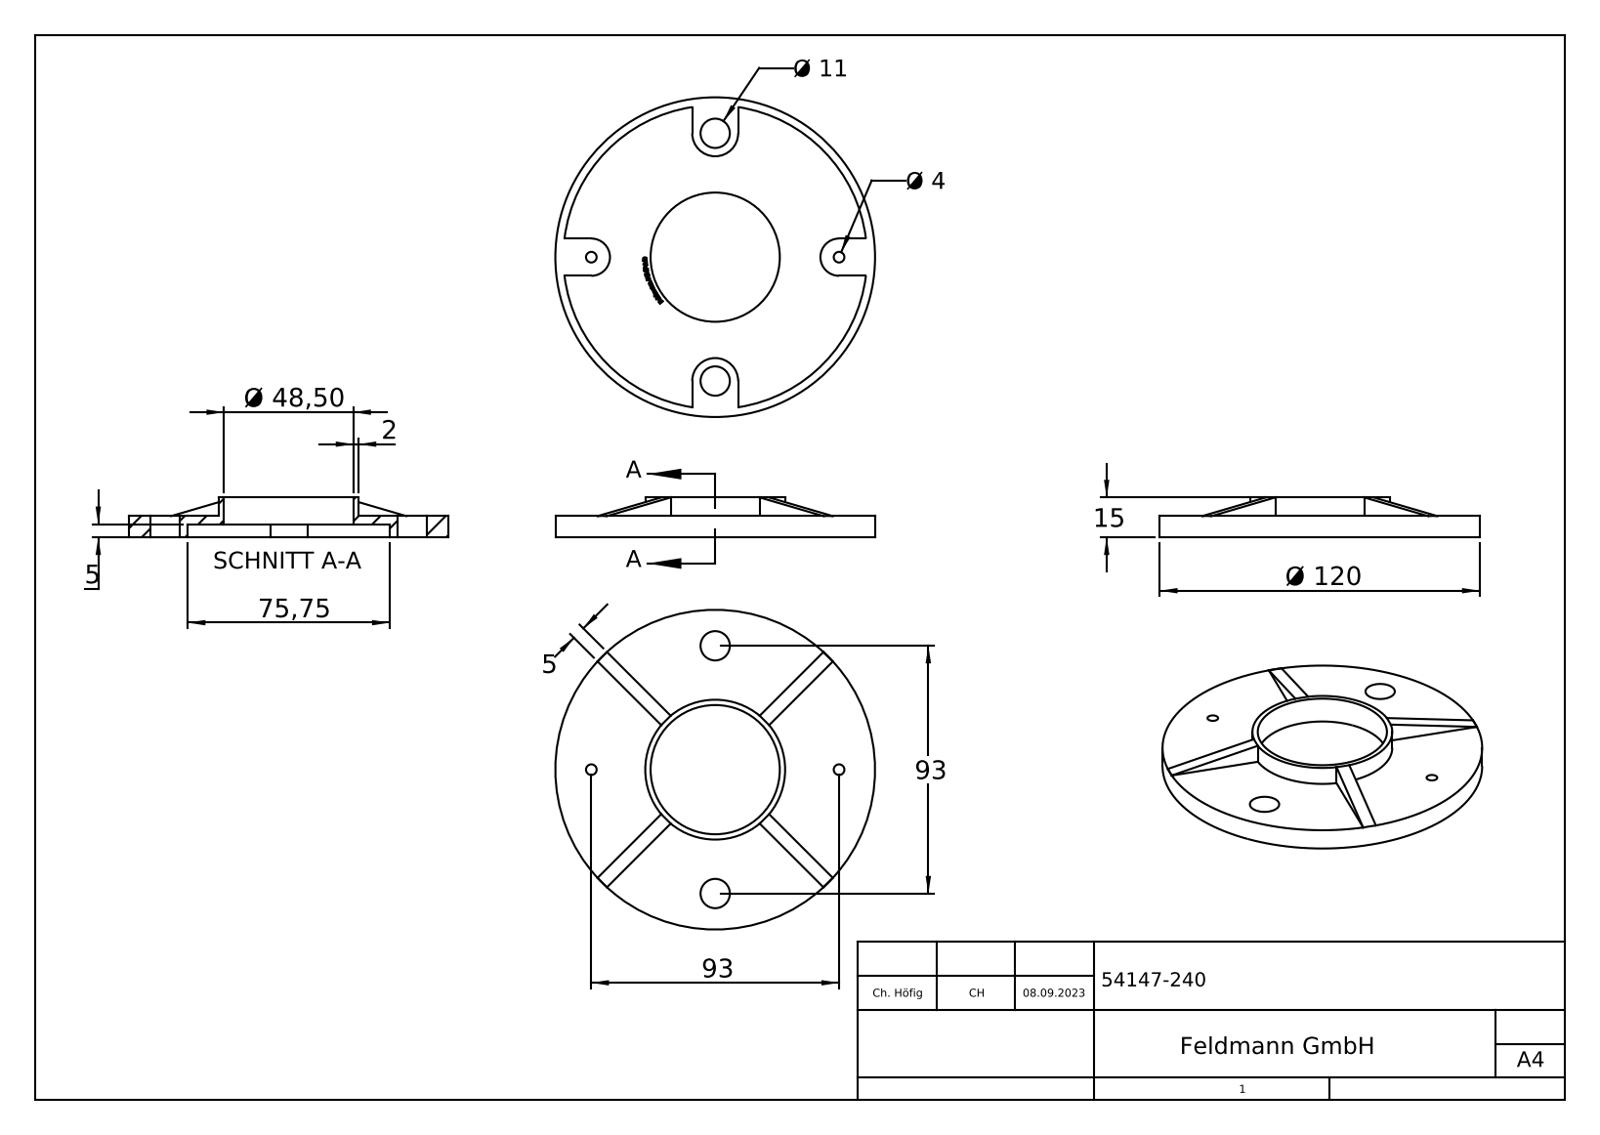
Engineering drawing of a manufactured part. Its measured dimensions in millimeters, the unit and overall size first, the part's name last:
Units: millimetres
Overall size (bounding box): 120 × 120 × 15
Round holes (diameter × count): ⌀4 ×2, ⌀11 ×2, ⌀60.5 ×1, ⌀114 ×1
Round bosses / shafts (diameter × count): ⌀120 ×1, ⌀64.5 ×1
Partial cylindrical surfaces — rounded edges, fillets, slot ends (radius × count): R7 ×2, R8.62 ×2
Main face-to-face distances: 3, 5, 8, 15, 10, 7, 14, 17.25, 17.26, 5.1
Hole centre spacings: 46.5, 65.76, 93
Volume: 38 943 mm³ · Surface area: 26 561 mm²
Bodies: 1 solid, 278 faces (172 planar, 18 cylindrical, 88 other)
Part name (STEP PRODUCT): 54148-240
STEP written by: SolidWorks 2018 (CONFIG_CONTROL_DESIGN)
